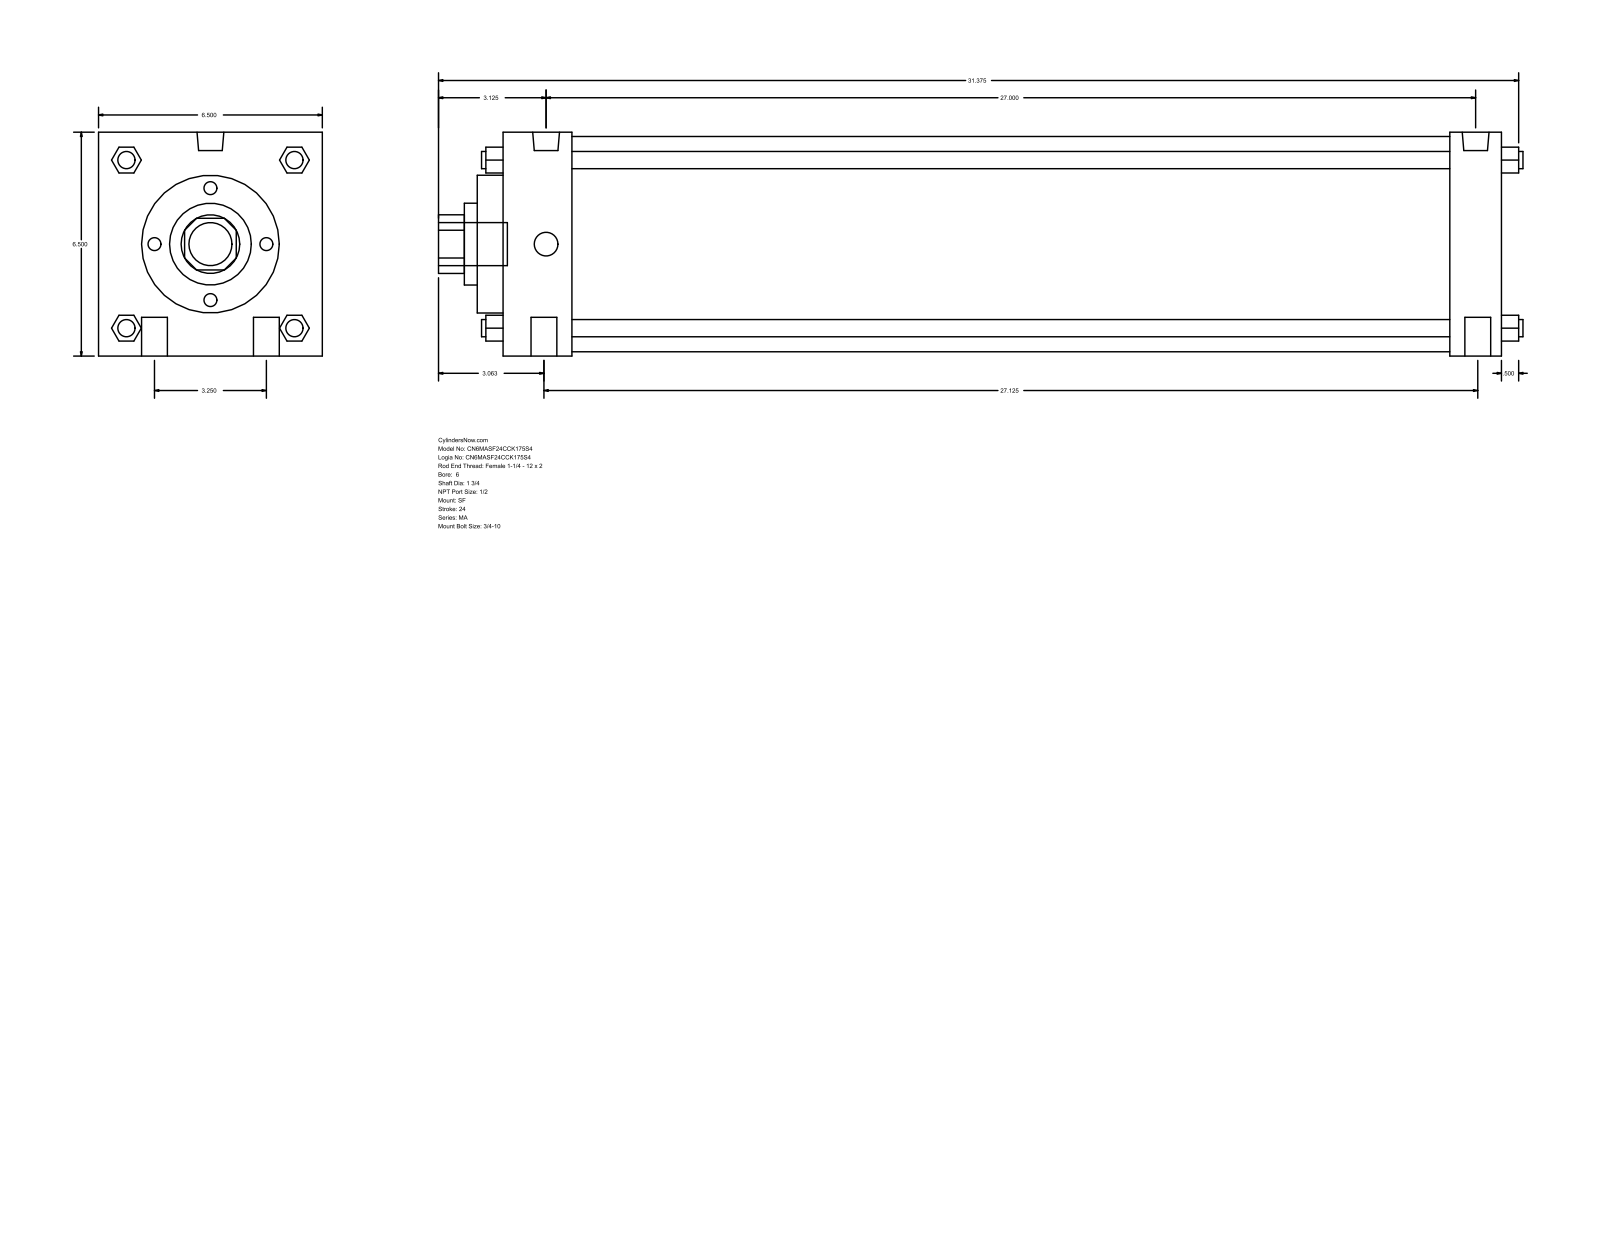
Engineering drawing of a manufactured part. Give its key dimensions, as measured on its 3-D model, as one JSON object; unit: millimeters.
{"part_name": "MA_SF__0600_1.75", "step_written_by": "GSSL Pune (CONFIG_CONTROL_DESIGN)", "units": "millimeters", "bodies": {"solids": 0, "faces": 126, "planar": 95, "cylindrical": 31, "other": 0}, "overall_size": [800.1, 165.1, 165.1], "round_holes": [[44.45, 1], [60.33, 1], [101.6, 1], [158.75, 1]], "round_bosses_or_shafts": [[19.05, 4], [12.7, 4], [19.77, 2], [17.46, 2], [31.75, 1]], "partial_cylinders_radius": [[21.63, 1]], "face_to_face_distances": [165.1, 736.61, 19.05, 50.8, 698.5, 38.11, 647.7, 685.81, 69.85, 717.55]}
